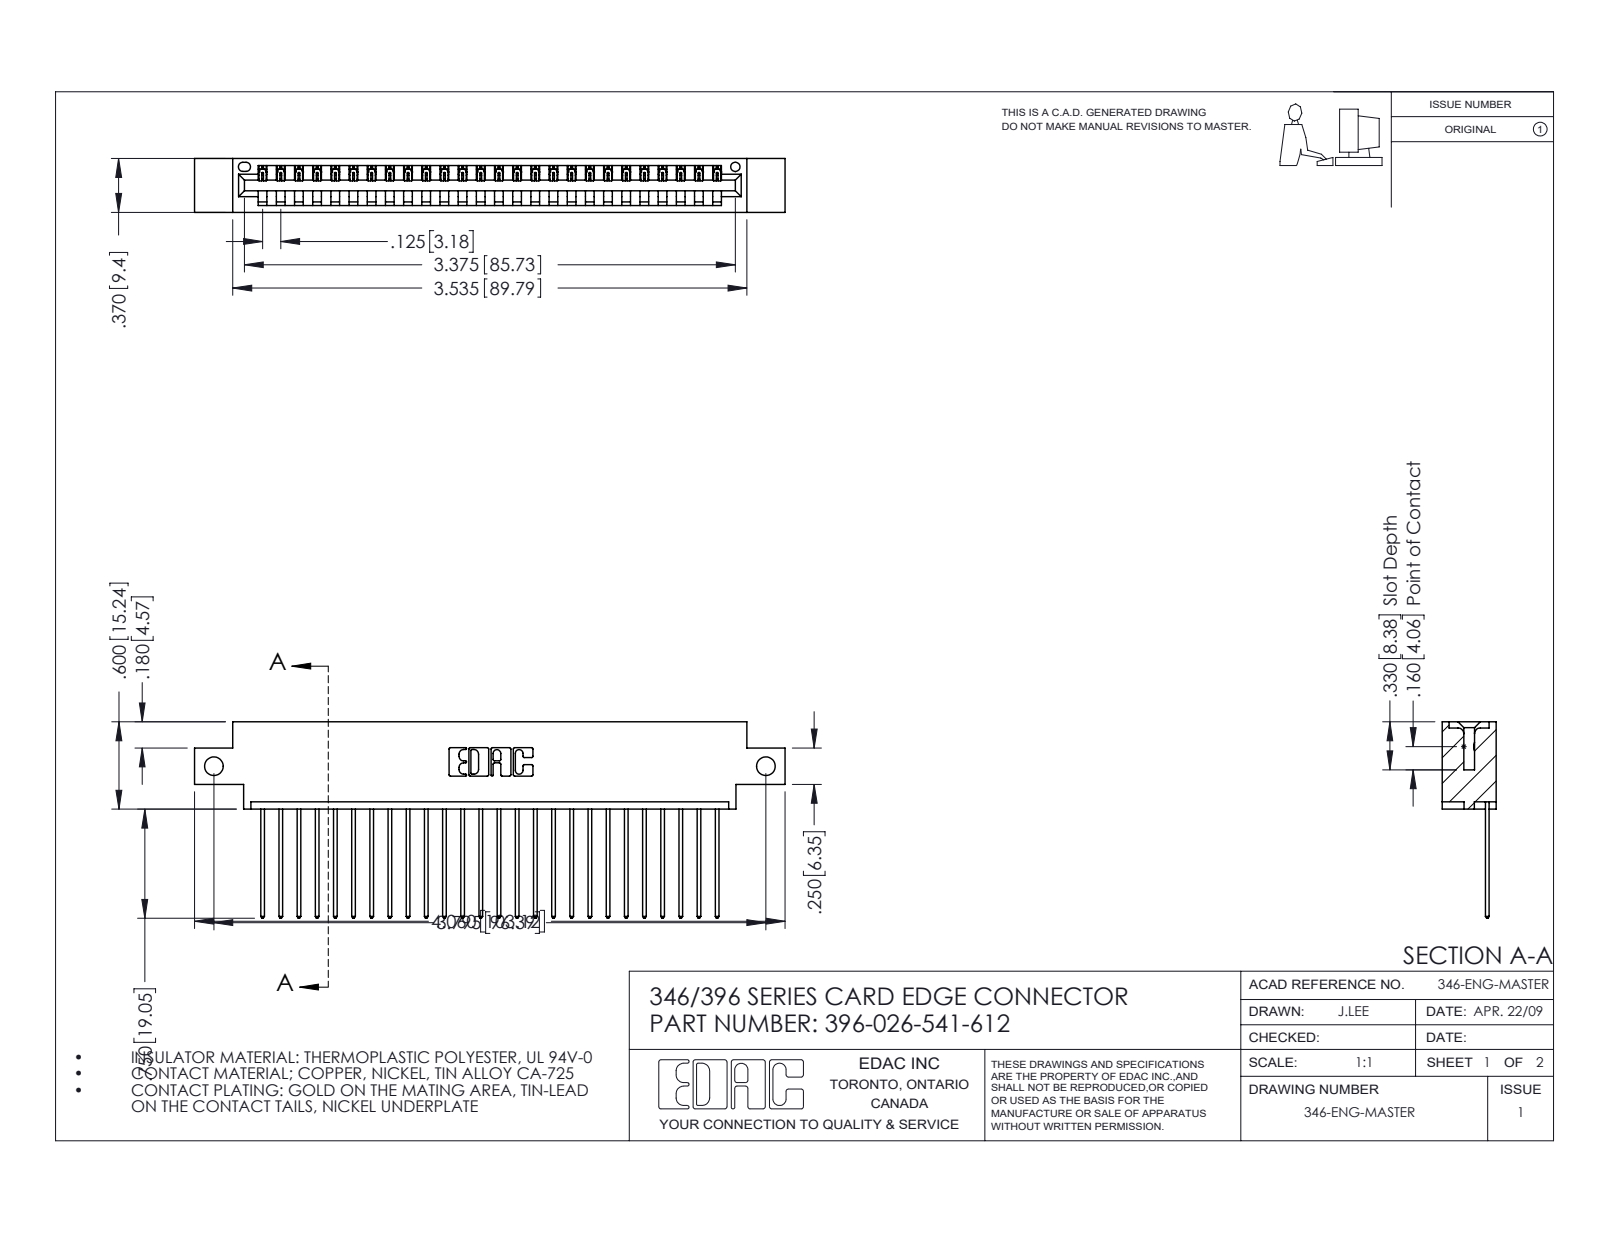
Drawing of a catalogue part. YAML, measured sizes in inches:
part_name: "346 Part_0.170 Offset - Side Mount; 396-026-541-612; 345-292-001_345-293-141"
step_written_by: "SolidWorks 2016 (CONFIG_CONTROL_DESIGN)"
units: inches
bodies: {solids: 27, faces: 1634, planar: 1120, cylindrical: 514, other: 0}
overall_size: [4.06, 1.35, 0.37]
volume: 0.586
surface_area: 19.16
round_holes:
  - {diameter: 0.128, count: 2}
  - {diameter: 0.064, count: 1}
partial_cylinders:
  - {radius: 0.006, count: 52}
  - {radius: 0.01, count: 52}
  - {radius: 0.01, count: 22}
  - {radius: 0.007, count: 6}
  - {radius: 0.031, count: 6}
  - {radius: 0.026, count: 3}
  - {radius: 0.031, count: 2}
  - {radius: 0.04, count: 2}
face_to_face_distances: [0.048, 0.322, 0.37, 0.25, 0.072, 0.298, 0.025, 0.148, 0.222, 0.1]
hole_center_spacings: [3.795]
